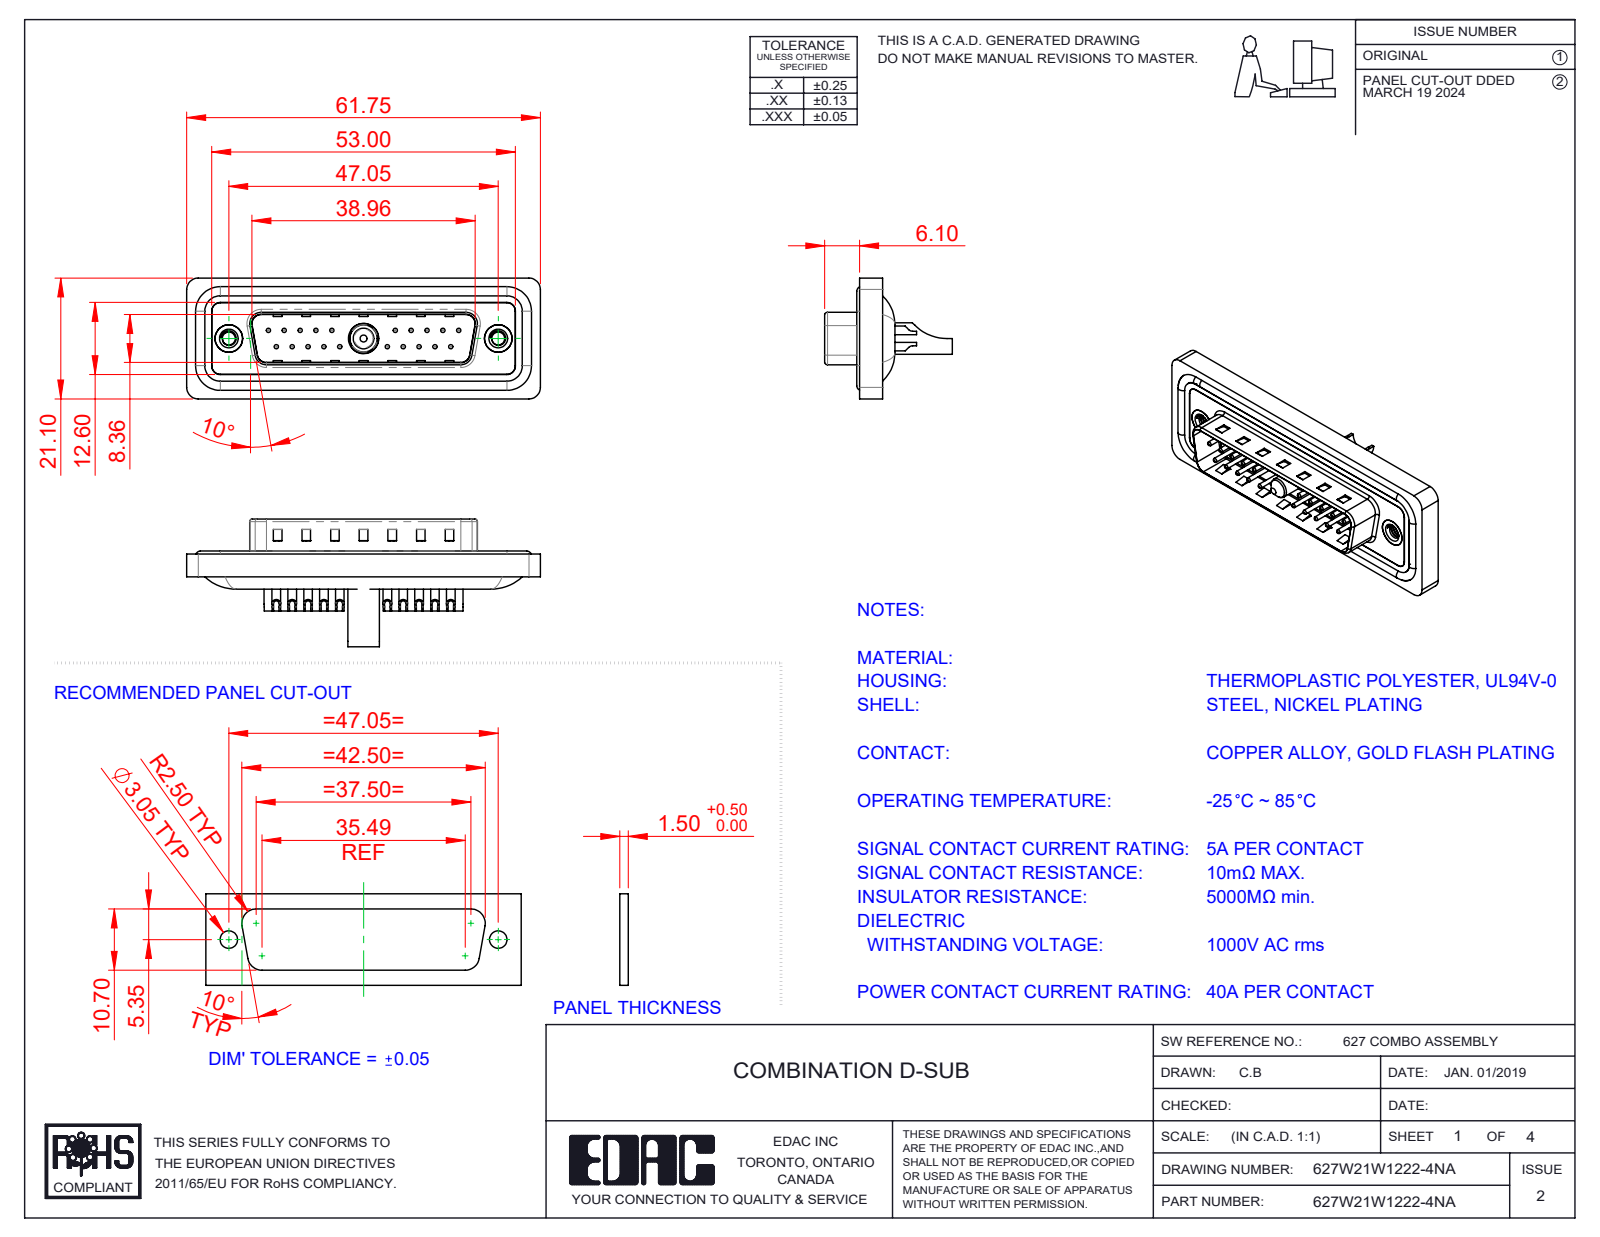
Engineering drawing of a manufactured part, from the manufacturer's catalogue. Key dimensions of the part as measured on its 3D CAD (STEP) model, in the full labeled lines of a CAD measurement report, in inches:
Part name (STEP PRODUCT): Power Pin_40A SC; 627Combo Waterproof Housing_25 Contacts; 627Combo Housing_21W1; 627Combo Contact Row 1_22 (+5 more)
STEP written by: SolidWorks 2023 (CONFIG_CONTROL_DESIGN)
Units: inches
Bodies: 29 solids, 1264 faces (401 planar, 530 cylindrical, 333 other)
Overall size (bounding box): 2.431 × 0.878 × 0.831
Volume: 0.444 in³ · Surface area: 18.99 in²
Round holes (diameter × count): ⌀0.03 ×20, ⌀0.039 ×20, ⌀0.063 ×20, ⌀0.079 ×20, ⌀0.089 ×2, ⌀0.157 ×2, ⌀0.189 ×2, ⌀0.197 ×2, ⌀0.181 ×1, ⌀0.191 ×1, ⌀0.209 ×1
Round bosses / shafts (diameter × count): ⌀0.059 ×20, ⌀0.063 ×4, ⌀0.193 ×2, ⌀0.217 ×1, ⌀0.205 ×1, ⌀0.187 ×1, ⌀0.148 ×1, ⌀0.142 ×1
Partial cylindrical surfaces — rounded edges, fillets, slot ends (radius × count): R0.059 ×22, R0.079 ×18, R0.02 ×8, R0.063 ×8, R0.039 ×6, R0.01 ×4, R0.024 ×4, R0.026 ×4
Main face-to-face distances: 0.016, 0.059, 0.043, 0.063, 0.02, 0.122, 0.114, 0.161, 0.032, 0.377
Hole centre spacings: 0.124, 0.109, 0.218, 0.327, 0.198, 0.763, 0.826, 0.872
